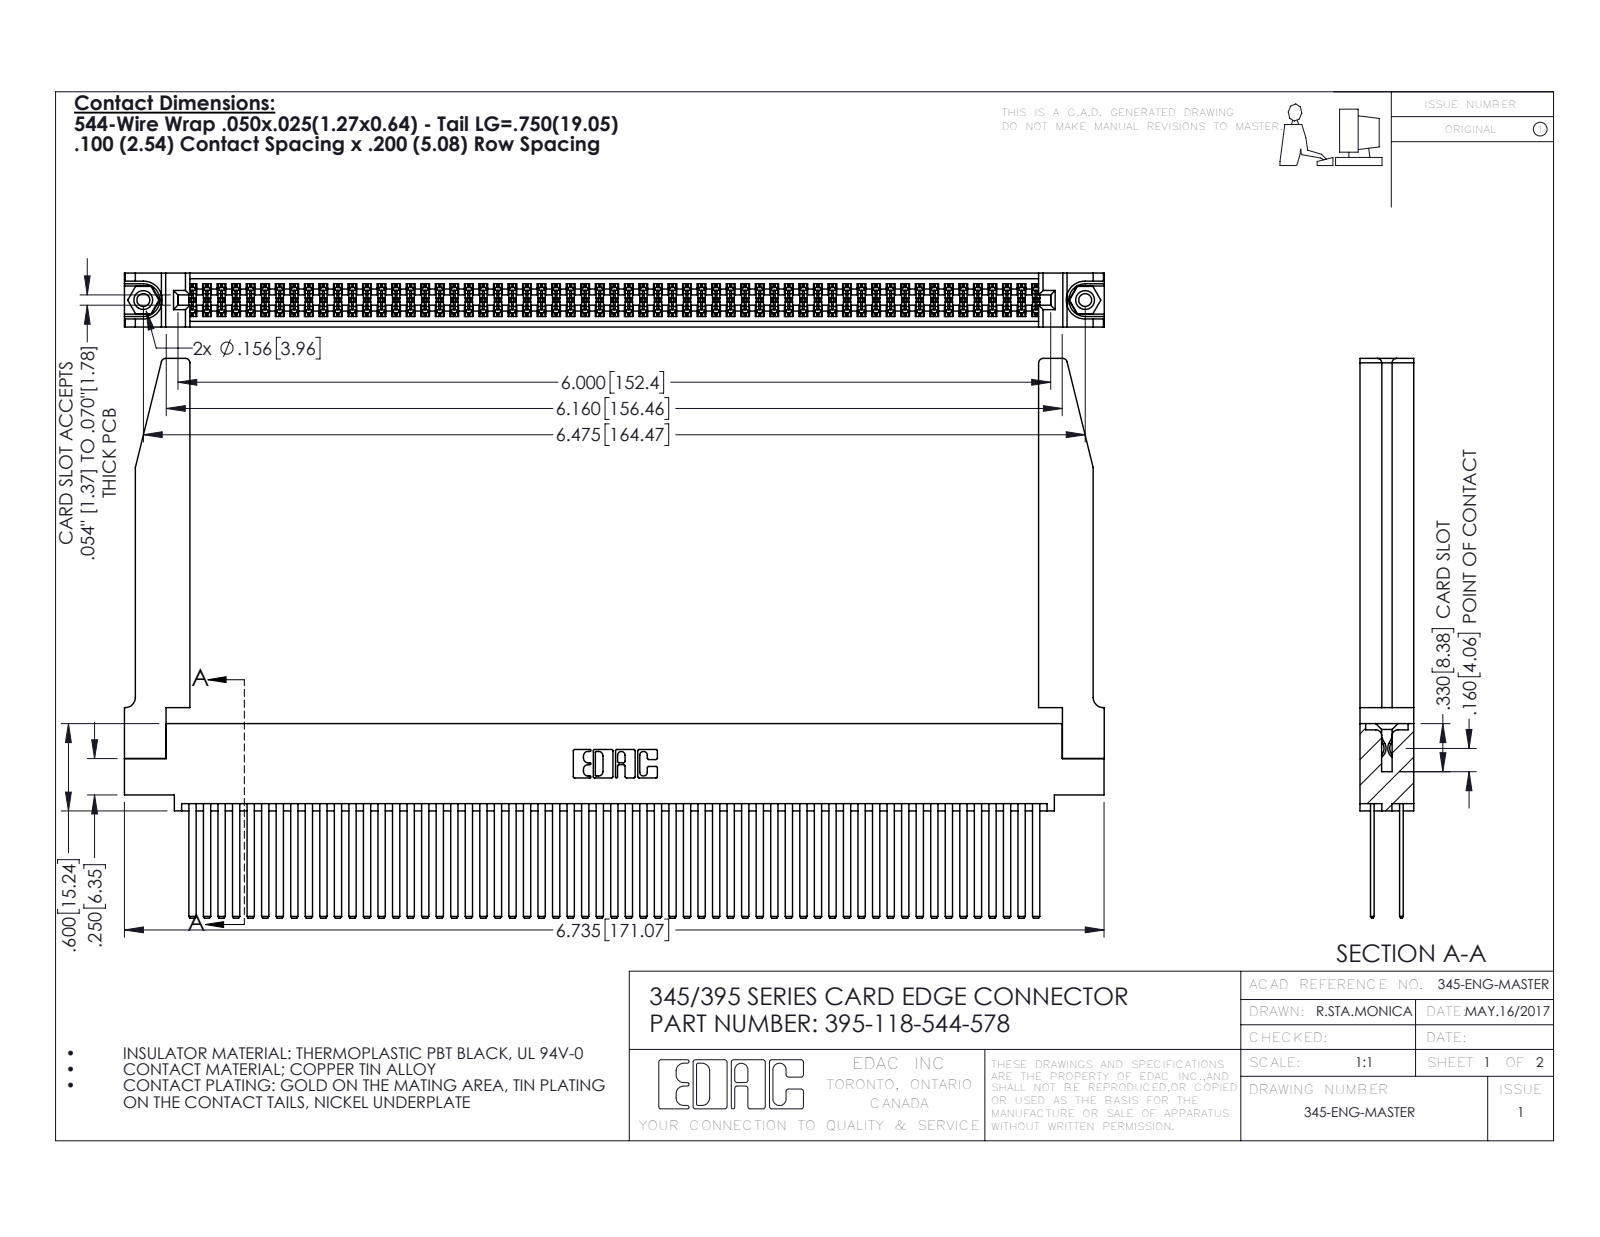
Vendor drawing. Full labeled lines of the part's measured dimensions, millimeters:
Part name (STEP PRODUCT): 345-250-001_345-250-001-102; 345 Part_0.110 Offset - 0.156 Dia-TH; 345-220-078_345-220-078; 395-118-544-578 (+1 more)
STEP written by: SolidWorks 2016 (CONFIG_CONTROL_DESIGN)
Units: millimetres
Bodies: 123 solids, 5556 faces (3648 planar, 1856 cylindrical, 52 other)
Overall size (bounding box): 171.1 × 97.7 × 9.4
Volume: 26 140 mm³ · Surface area: 39 250 mm²
Round holes (diameter × count): ⌀2.3 ×2, ⌀3.2 ×2, ⌀4 ×2, ⌀1.6 ×1
Round bosses / shafts (diameter × count): ⌀3.9 ×2
Partial cylindrical surfaces — rounded edges, fillets, slot ends (radius × count): R0.2 ×177, R0.3 ×22, R0.8 ×8, R0.2 ×6, R0.8 ×6, R0.7 ×3, R0.4 ×2, R0.5 ×2
Main face-to-face distances: 1.8, 7.6, 2.5, 6.9, 0.6, 5.1, 9.4, 5.7, 4.4, 3.8
Hole centre spacings: 6.9, 158.5, 164.5
